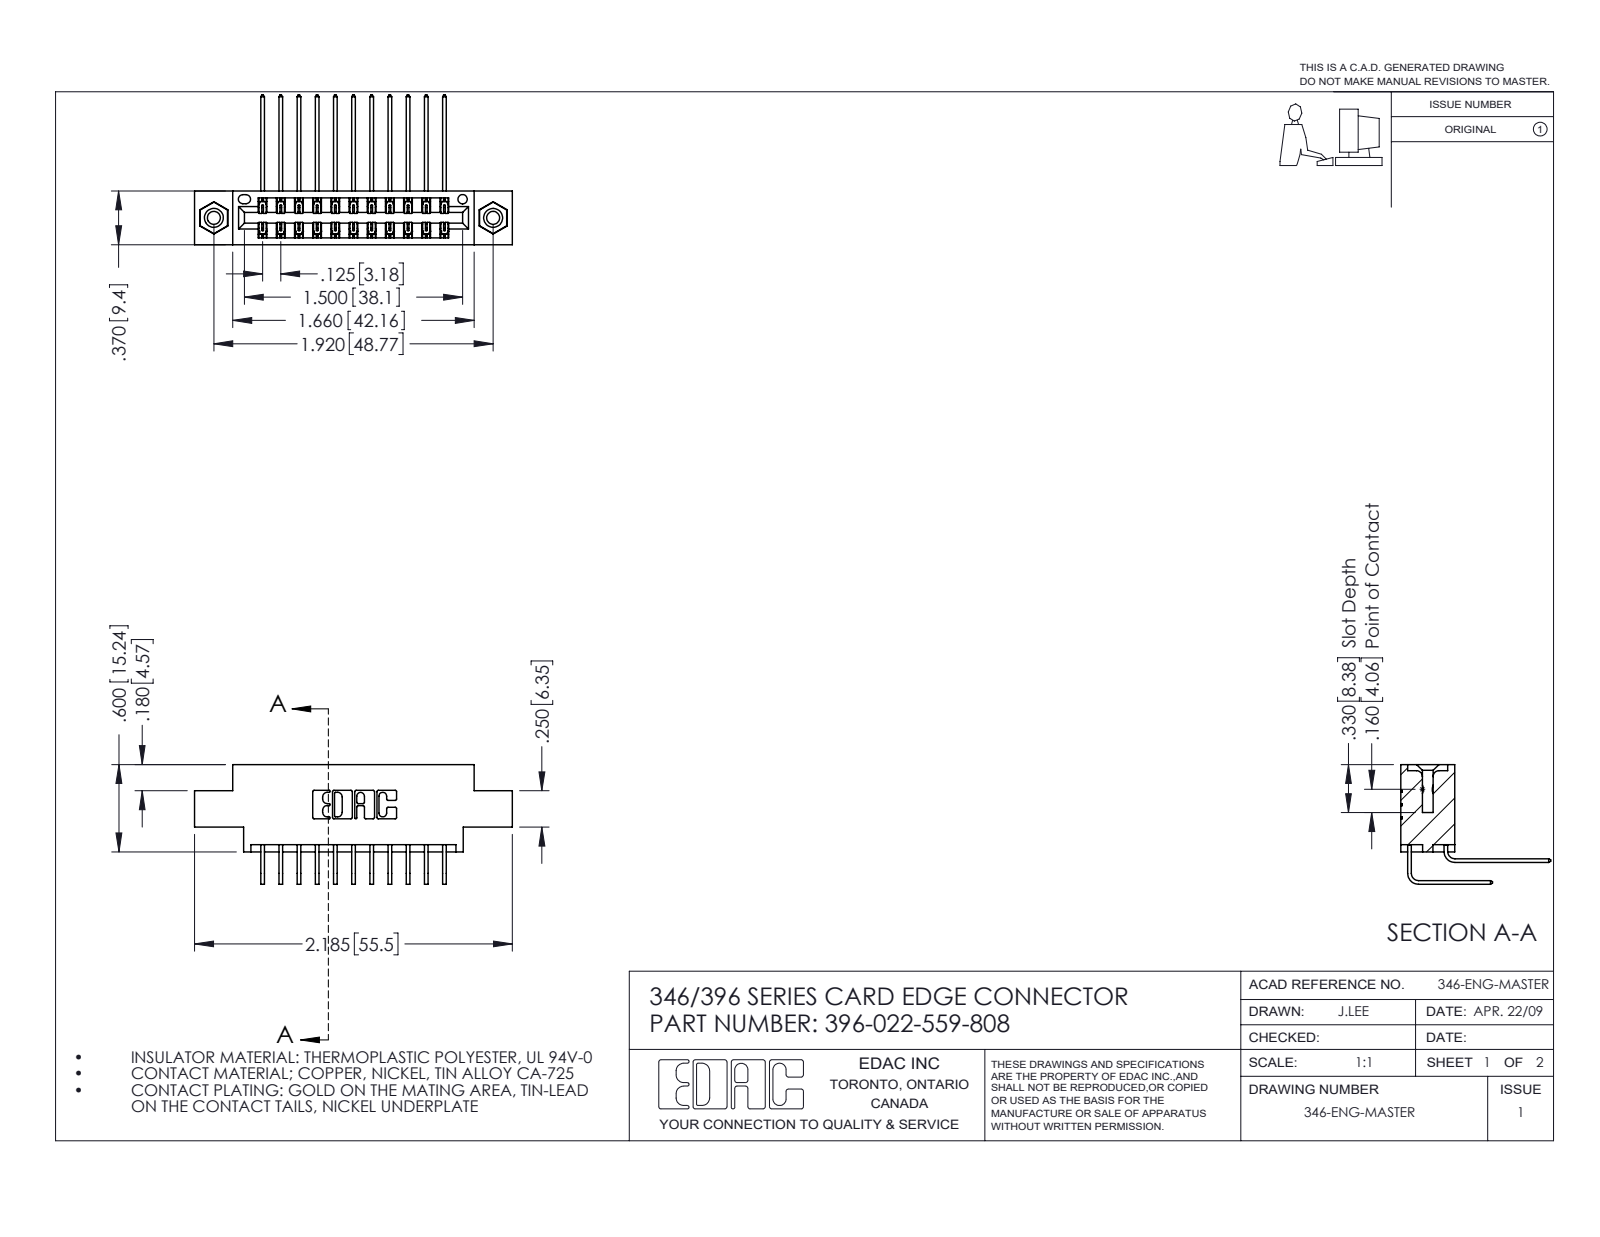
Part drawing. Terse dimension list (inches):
name: 345-292-001_559 Tail - 2; 345-250-001_345-250-003-102; 345-292-001_558 559 Tail - 1; 396-022-559-808 (+1 more)
written by: SolidWorks 2016 (CONFIG_CONTROL_DESIGN)
unit: in
bodies: 25 solids, 1374 faces (926 planar, 432 cylindrical, 16 other)
size: 2.185 × 1.03 × 0.823
volume: 0.313 in³; area: 11.44 in²
holes: 2× ⌀0.089, 2× ⌀0.125, 2× ⌀0.156, 1× ⌀0.064
bosses: 2× ⌀0.155
rounds: 33× R0.006, 22× R0.01, 6× R0.007, 6× R0.031, 3× R0.026, 2× R0.014, 2× R0.022, 2× R0.024
face distances: 0.048, 0.25, 0.322, 0.37, 0.025, 0.072, 0.298, 0.222, 0.148, 0.275
hole spacings: 0.246, 1.715, 1.92
